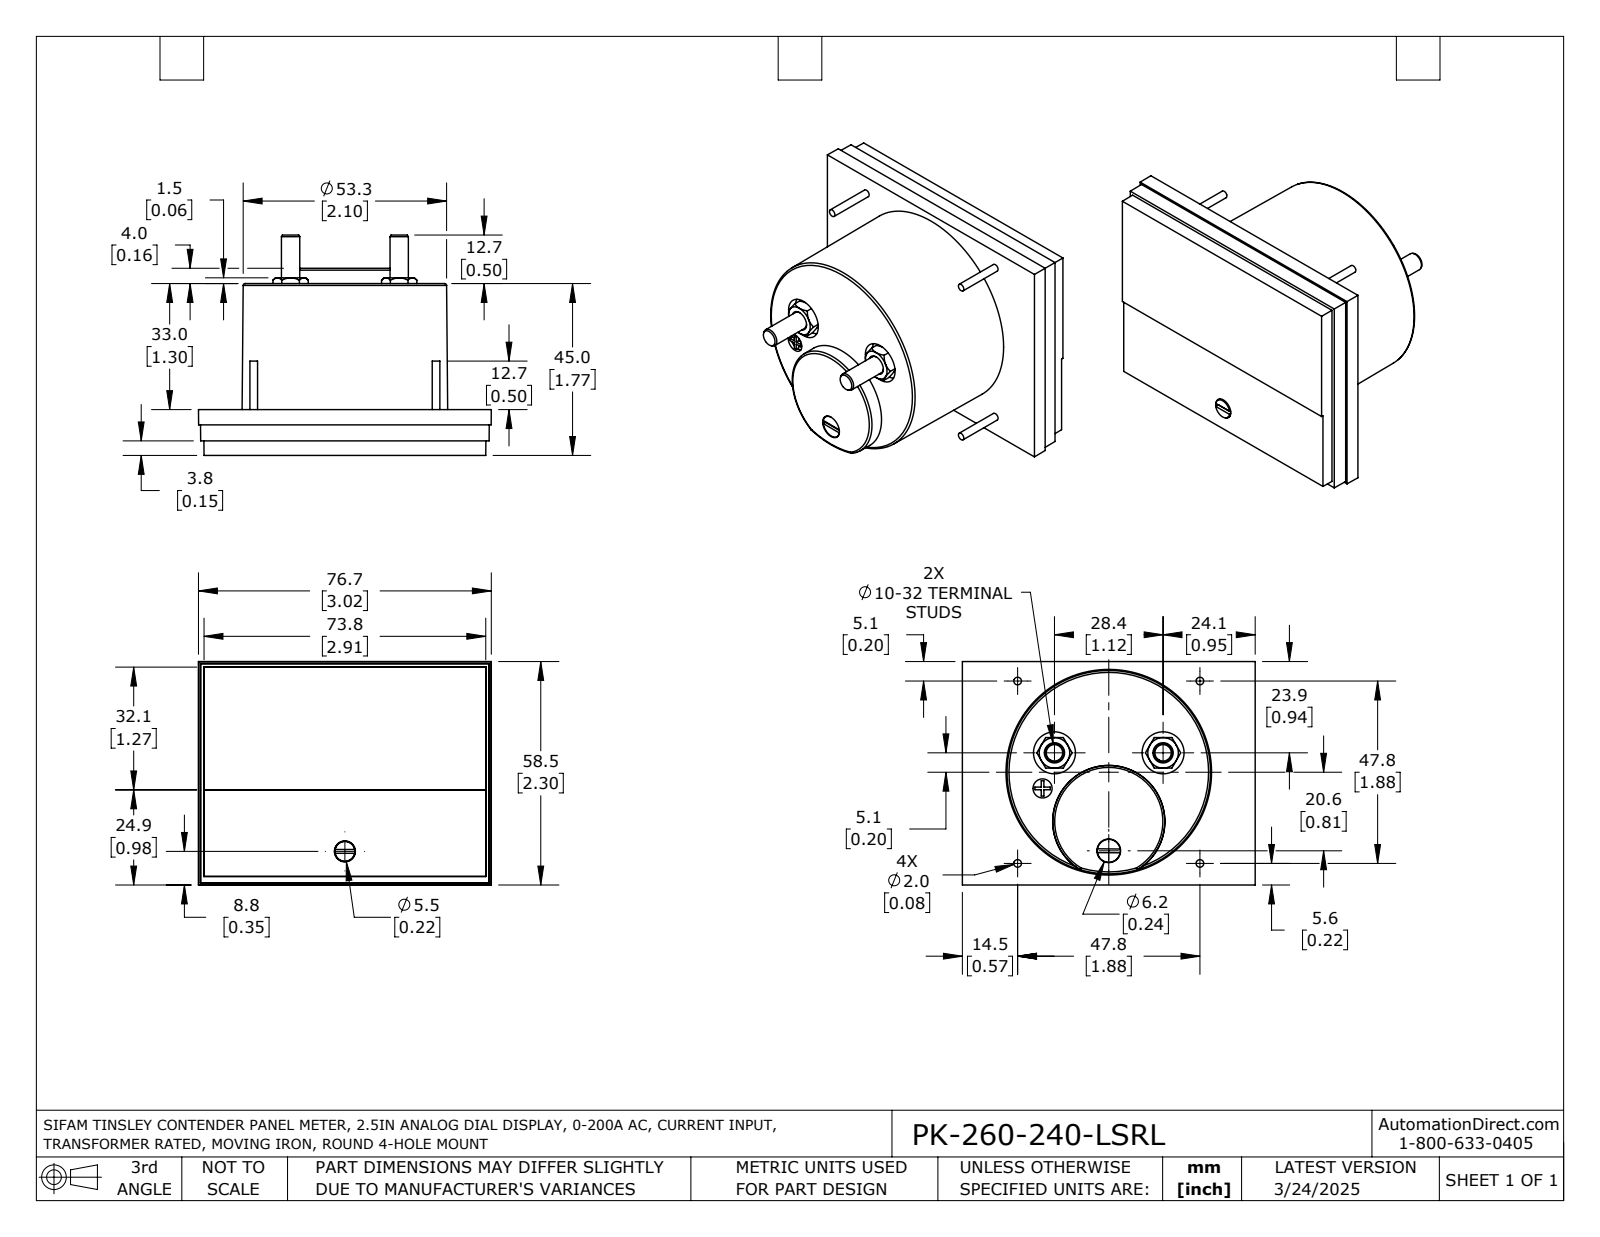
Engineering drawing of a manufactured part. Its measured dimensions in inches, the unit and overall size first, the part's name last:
Units: inches
Overall size (bounding box): 3.02 × 2.303 × 2.272
Round holes (diameter × count): ⌀0.197 ×3, ⌀0.433 ×2, ⌀0.209 ×1, ⌀0.217 ×1, ⌀0.244 ×1
Round bosses / shafts (diameter × count): ⌀0.079 ×4, ⌀0.189 ×2, ⌀0.236 ×1, ⌀0.205 ×1
Partial cylindrical surfaces — rounded edges, fillets, slot ends (radius × count): R0.033 ×1
Main face-to-face distances: 0.02, 0.472, 0.13, 0.322, 0.15, 0.453, 0.057, 0.077, 0.396, 0.073
Hole centre spacings: 1.155, 1.16, 0.387, 0.938, 0.942, 1.12, 1.295
Volume: 7.657 in³ · Surface area: 36.55 in²
Bodies: 1 solid, 192 faces (95 planar, 37 cylindrical, 60 other)
Part name (STEP PRODUCT): PK-260-240-LSRL
STEP written by: SolidWorks 2021 (AUTOMOTIVE_DESIGN)
